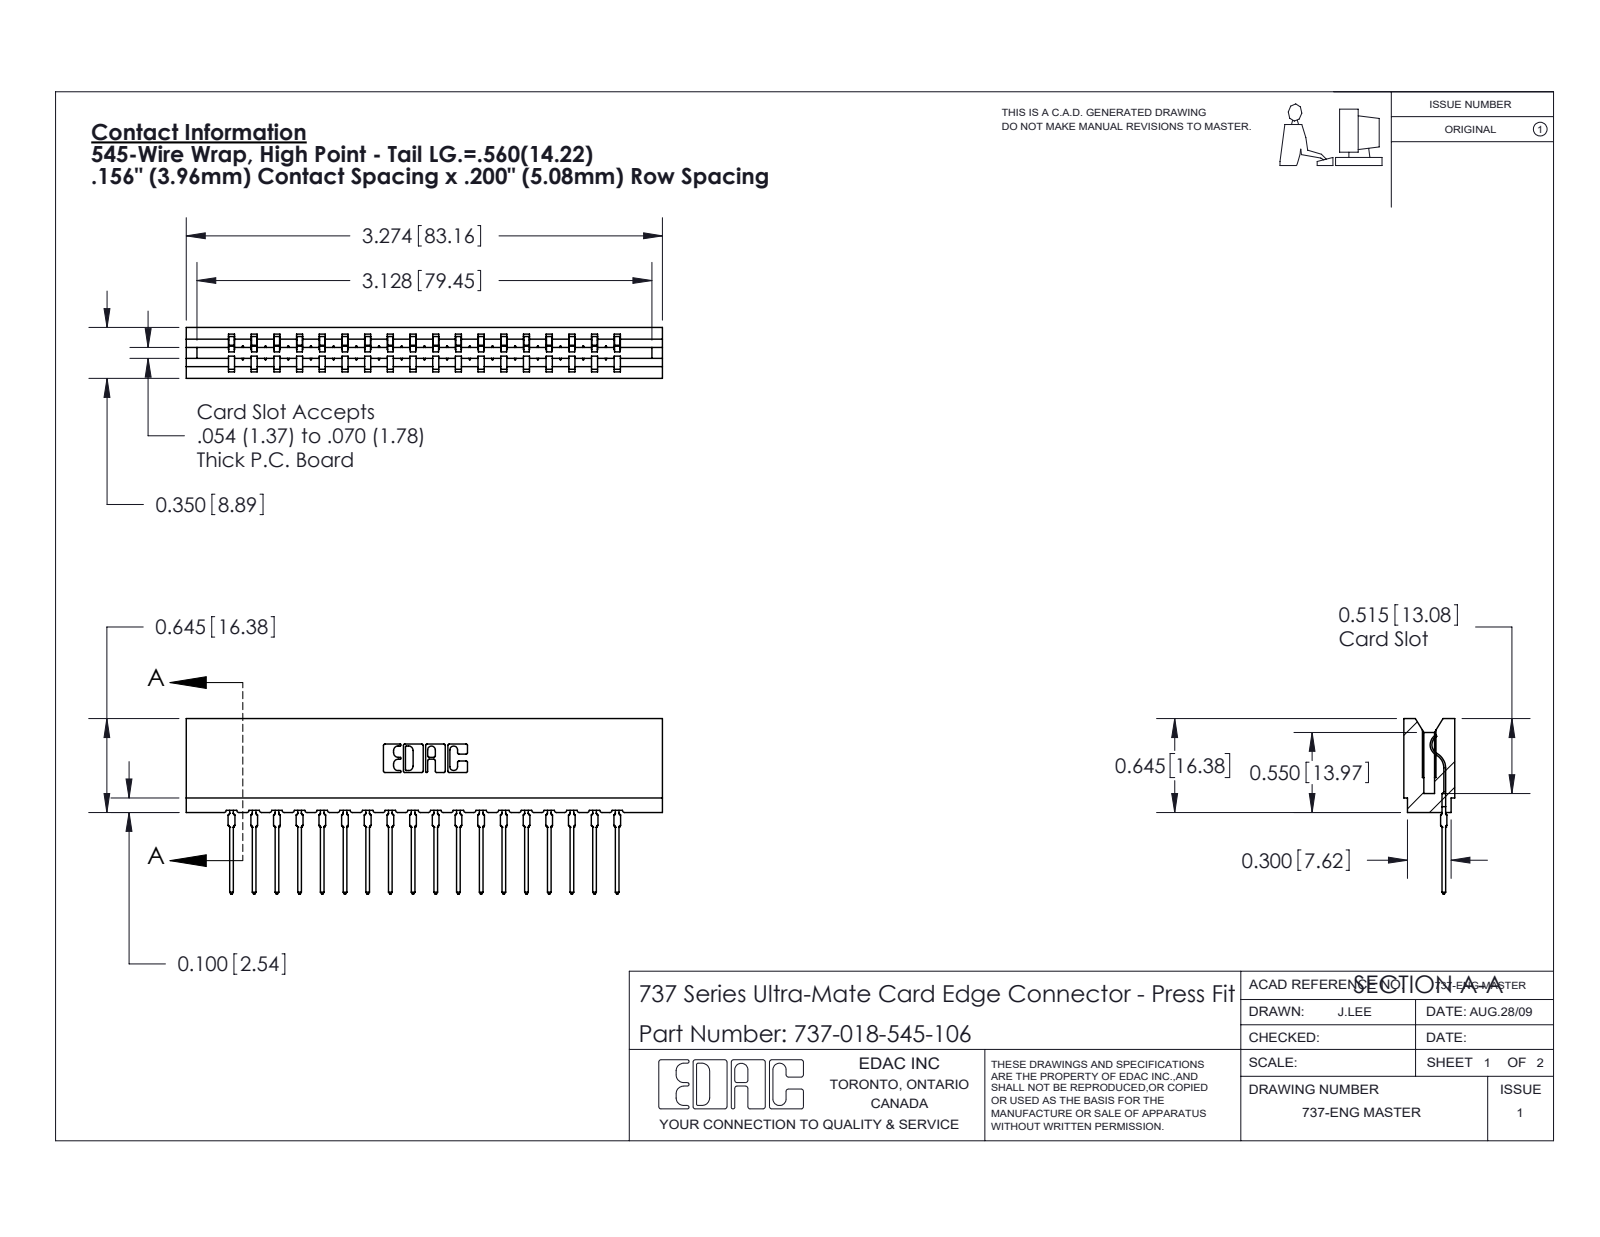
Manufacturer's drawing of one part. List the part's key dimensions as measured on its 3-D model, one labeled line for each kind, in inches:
Part name (STEP PRODUCT): 737 Part_Insulator Option - 06; 737-018-545-106; 745-292-001_545
STEP written by: SolidWorks 2020 (CONFIG_CONTROL_DESIGN)
Units: inches
Bodies: 19 solids, 2129 faces (1279 planar, 382 cylindrical, 468 other)
Overall size (bounding box): 3.274 × 1.206 × 0.35
Volume: 0.503 in³ · Surface area: 16.93 in²
Partial cylindrical surfaces — rounded edges, fillets, slot ends (radius × count): R0.015 ×36, R0.021 ×36, R0.01 ×22, R0.007 ×6, R0.031 ×6, R0.005 ×4, R0.011 ×4, R0.026 ×3
Main face-to-face distances: 0.138, 0.212, 0.35, 0.156, 0.624, 0.78, 0.468, 0.312, 1.404, 0.074
